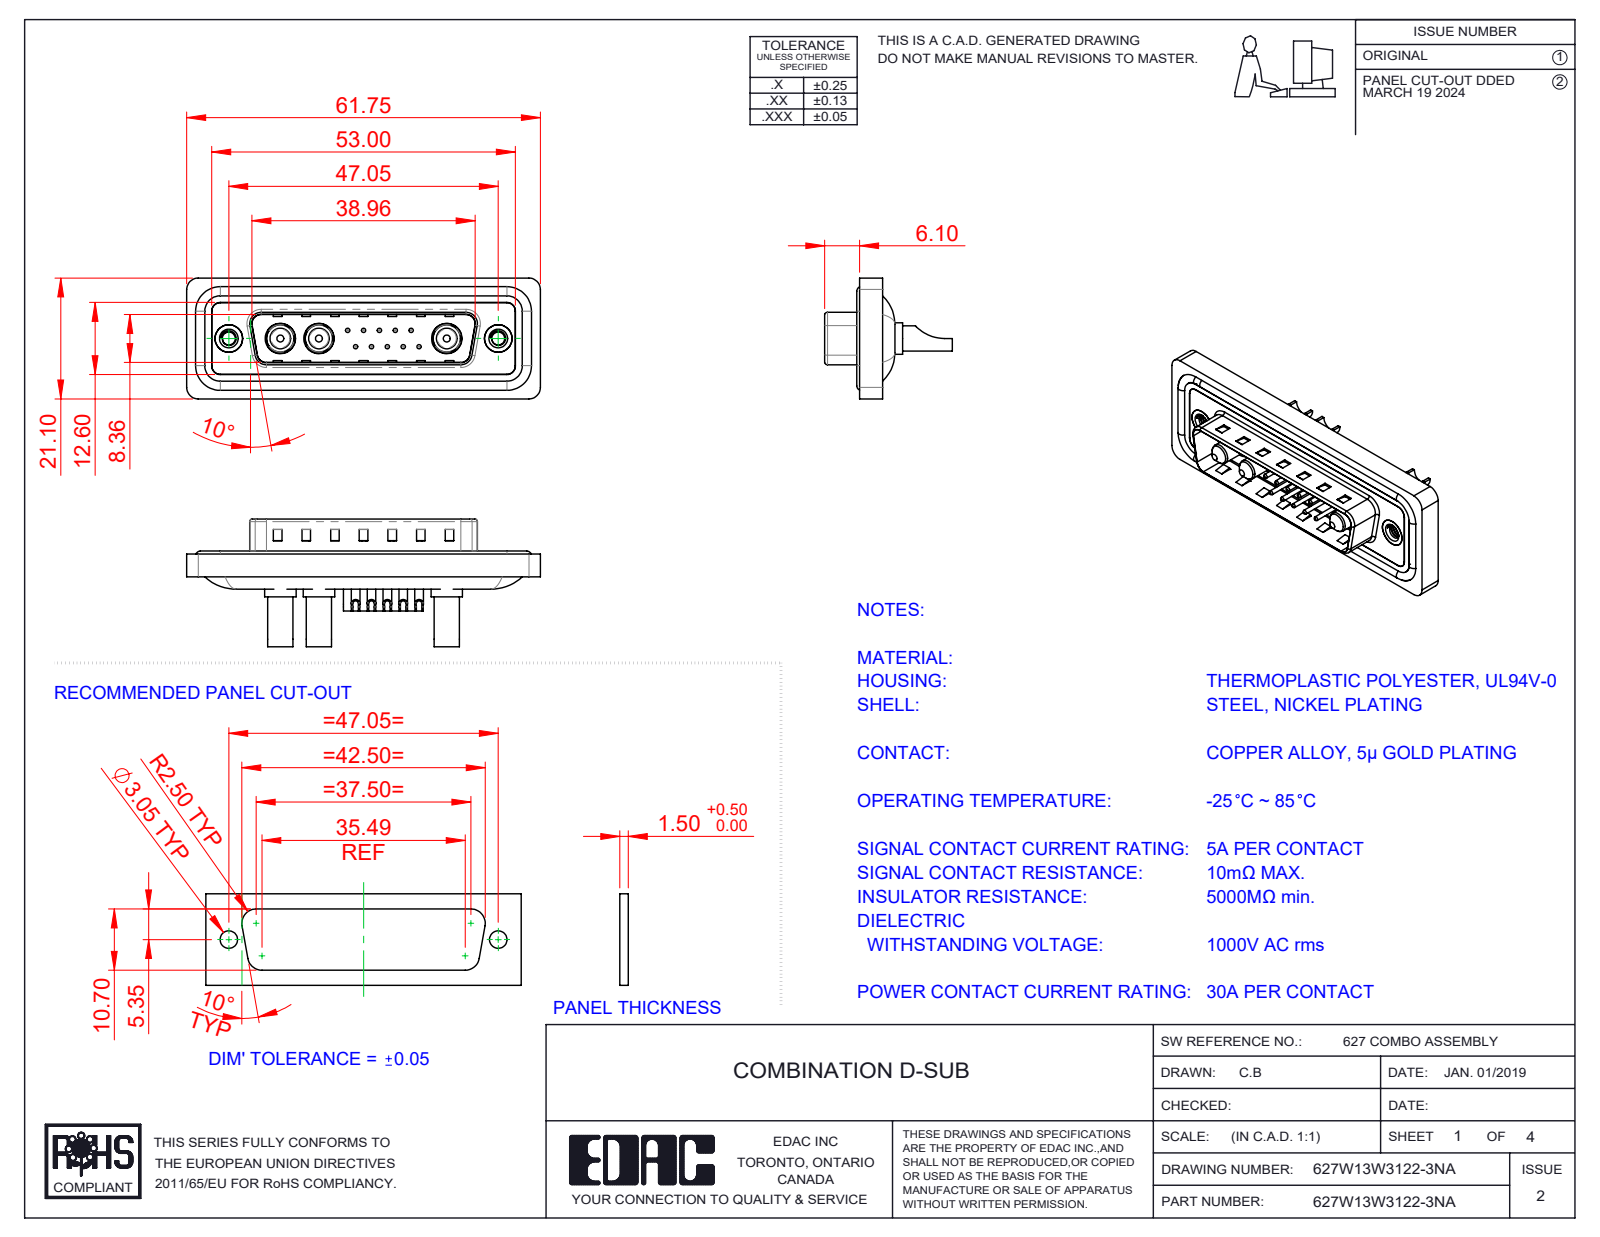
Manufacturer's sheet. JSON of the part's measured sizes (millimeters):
{"part_name": "Power Pin_30A SC; 627W13W3122-3NA; 627Combo Shell Rear_25 Contacts; 627Combo Waterproof Housing_25 Contacts (+5 more)", "step_written_by": "SolidWorks 2023 (CONFIG_CONTROL_DESIGN)", "units": "millimeters", "bodies": {"solids": 23, "faces": 986, "planar": 338, "cylindrical": 416, "other": 232}, "overall_size": [61.75, 22.3, 21.1], "volume_mm3": 7424, "surface_area_mm2": 12275, "round_holes": [[0.75, 10], [1, 10], [1.6, 10], [2, 10], [3.5, 3], [4.85, 3], [5.3, 3], [2.26, 2], [4, 2], [4.8, 2], [5, 2]], "round_bosses_or_shafts": [[1.5, 10], [1.6, 4], [5.5, 3], [5.2, 3], [4.75, 3], [4.4, 3], [3.75, 3], [3.6, 3]], "partial_cylinders_radius": [[1.5, 22], [2, 18], [0.5, 8], [1.6, 8], [1, 6], [0.25, 4], [0.6, 4], [0.65, 4]], "face_to_face_distances": [0.4, 1.5, 1.1, 1.6, 0.5, 3.1, 2.9, 0.82, 9.58, 4.1], "hole_center_spacings": [3.16, 2.77, 5.04, 5.54, 7.49, 5.03, 8.31, 10.11]}
